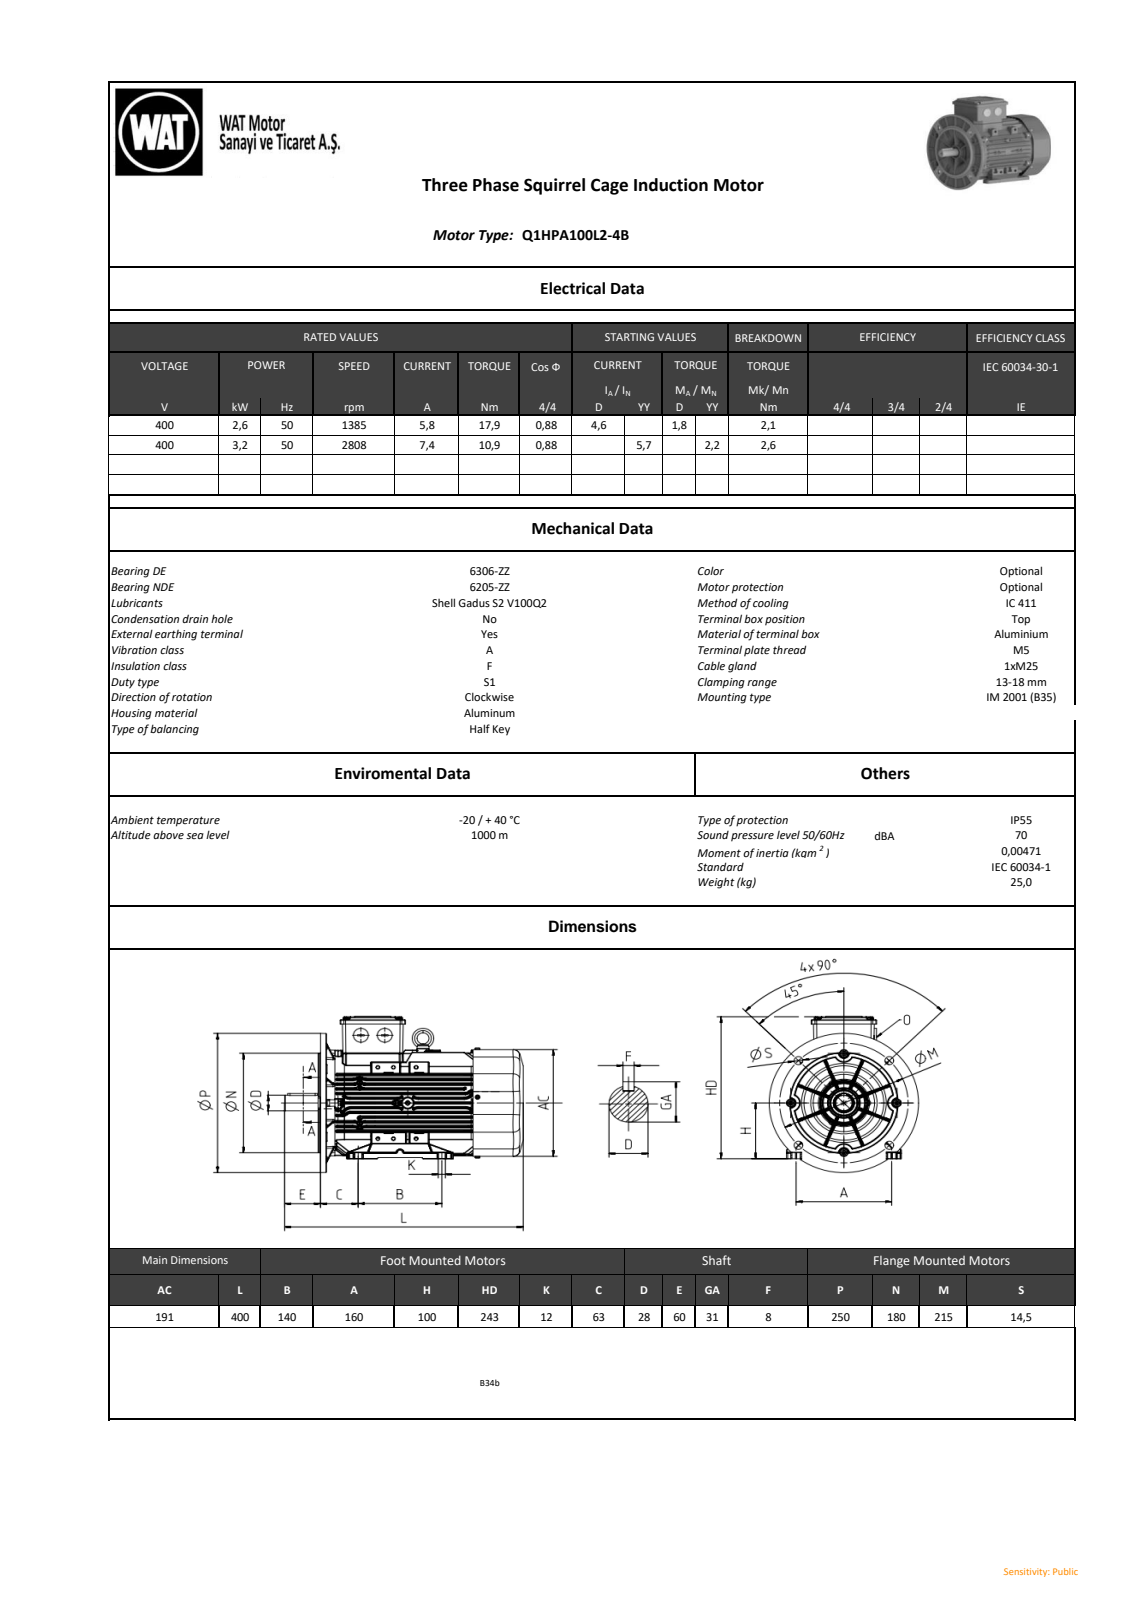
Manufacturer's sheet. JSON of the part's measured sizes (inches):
{"part_name": "QH series_ 100_B35_stp_objects", "step_written_by": "SIEMENS PLM Software NX2206.8101 (AUTOMOTIVE_DESIGN)", "units": "inches", "bodies": {"solids": 0, "faces": 6389, "planar": 1357, "cylindrical": 2468, "other": 2564}, "overall_size": [15.721, 11.05, 9.84], "round_holes": [[0.256, 4], [0.394, 1], [1.749, 1], [2.26, 1], [3.504, 1], [4.291, 1], [5.079, 1], [5.236, 1]], "round_bosses_or_shafts": [[0.315, 8], [0.472, 4], [0.335, 4], [0.236, 4], [0.197, 4], [0.984, 3], [7.087, 1], [4.469, 1]], "partial_cylinders_radius": [[0.039, 668], [0.031, 536], [0.079, 96], [0.059, 80], [0.098, 62], [0.02, 49], [0.032, 48], [0.197, 40]], "face_to_face_distances": [0.336, 0.333, 0.333, 3.002, 0.666, 3.679, 1.007, 0.671, 3.019, 2.348], "hole_center_spacings": [2.52, 2.623, 4.111, 5.039, 5.634]}
